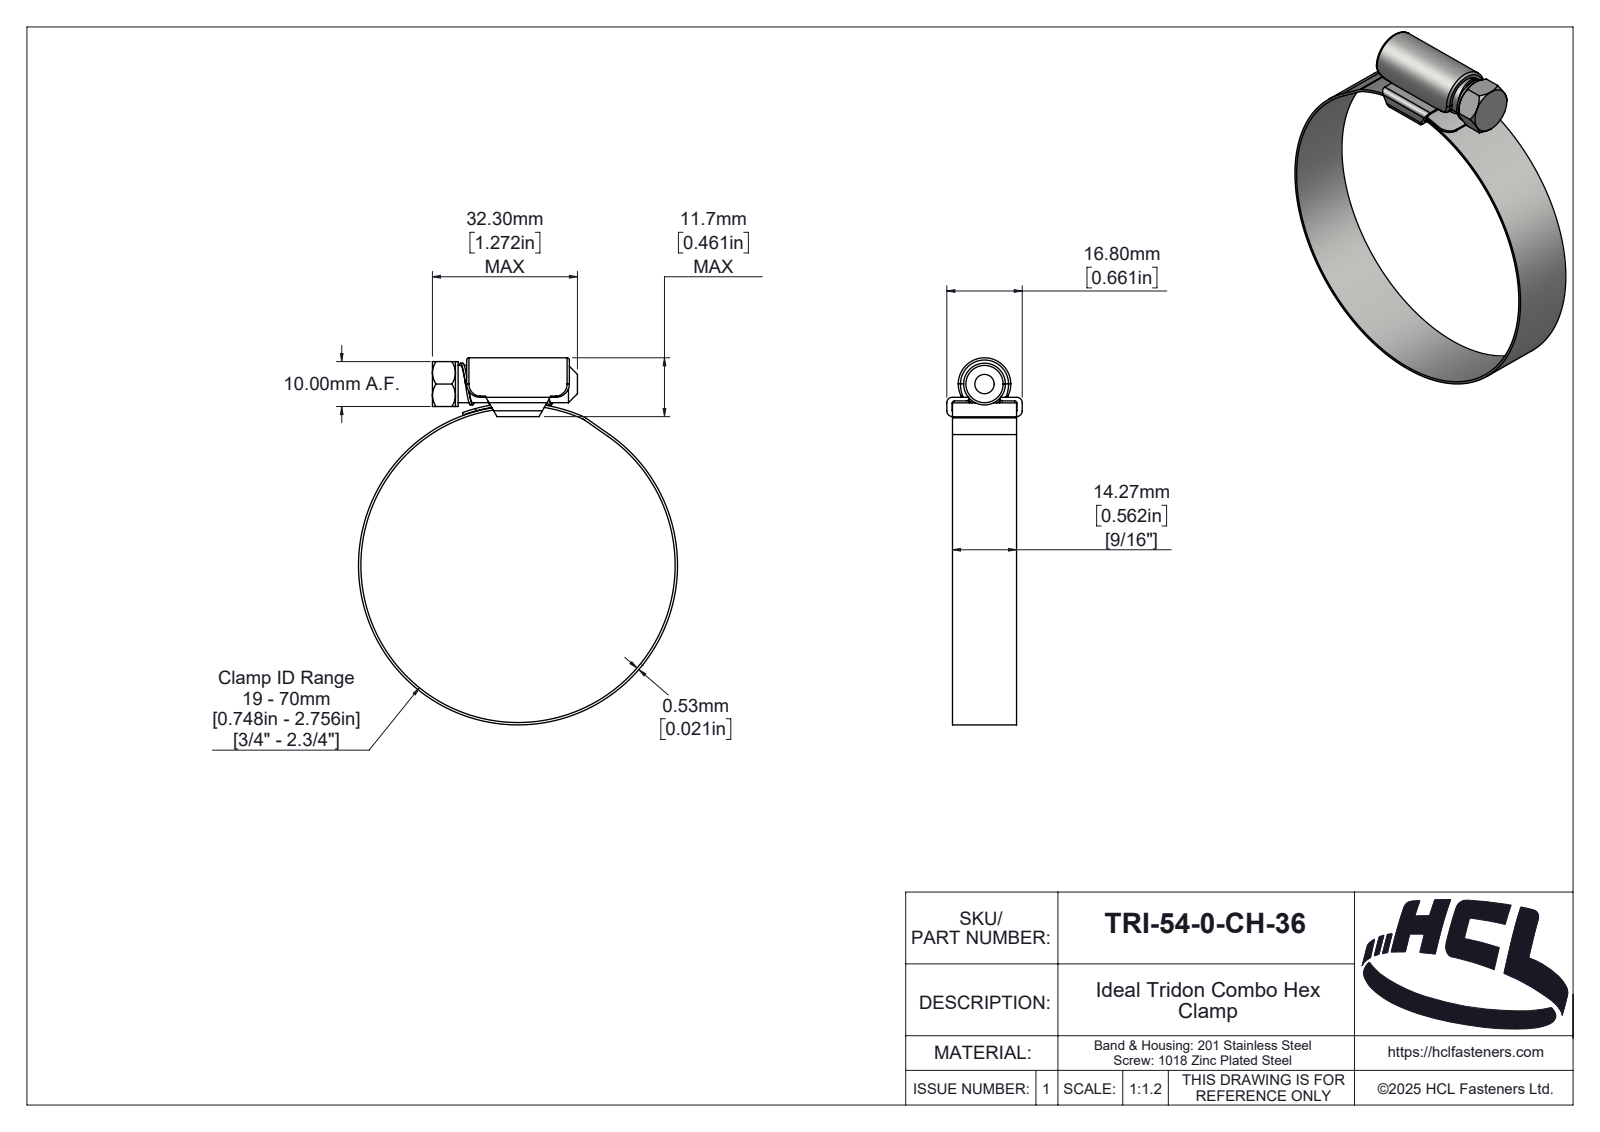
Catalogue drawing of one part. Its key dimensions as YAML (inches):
part_name: "TRI-54-0-CH-36"
step_written_by: "SolidWorks 2025 (AUTOMOTIVE_DESIGN)"
units: inches
bodies: {solids: 3, faces: 212, planar: 35, cylindrical: 101, other: 76}
overall_size: [3.218, 2.798, 0.661]
volume: 0.284
surface_area: 15.38
round_holes:
  - {diameter: 2.756, count: 1}
round_bosses_or_shafts:
  - {diameter: 2.798, count: 1}
  - {diameter: 0.394, count: 1}
  - {diameter: 0.327, count: 1}
partial_cylinders:
  - {radius: 0.02, count: 6}
  - {radius: 0.118, count: 4}
  - {radius: 0.004, count: 2}
  - {radius: 0.047, count: 2}
  - {radius: 0.051, count: 2}
  - {radius: 0.018, count: 1}
  - {radius: 0.074, count: 1}
  - {radius: 0.079, count: 1}
face_to_face_distances: [0.047, 0.561, 0.021, 0.138, 0.091, 0.169, 0.122, 0.031, 0.393, 0.05]
